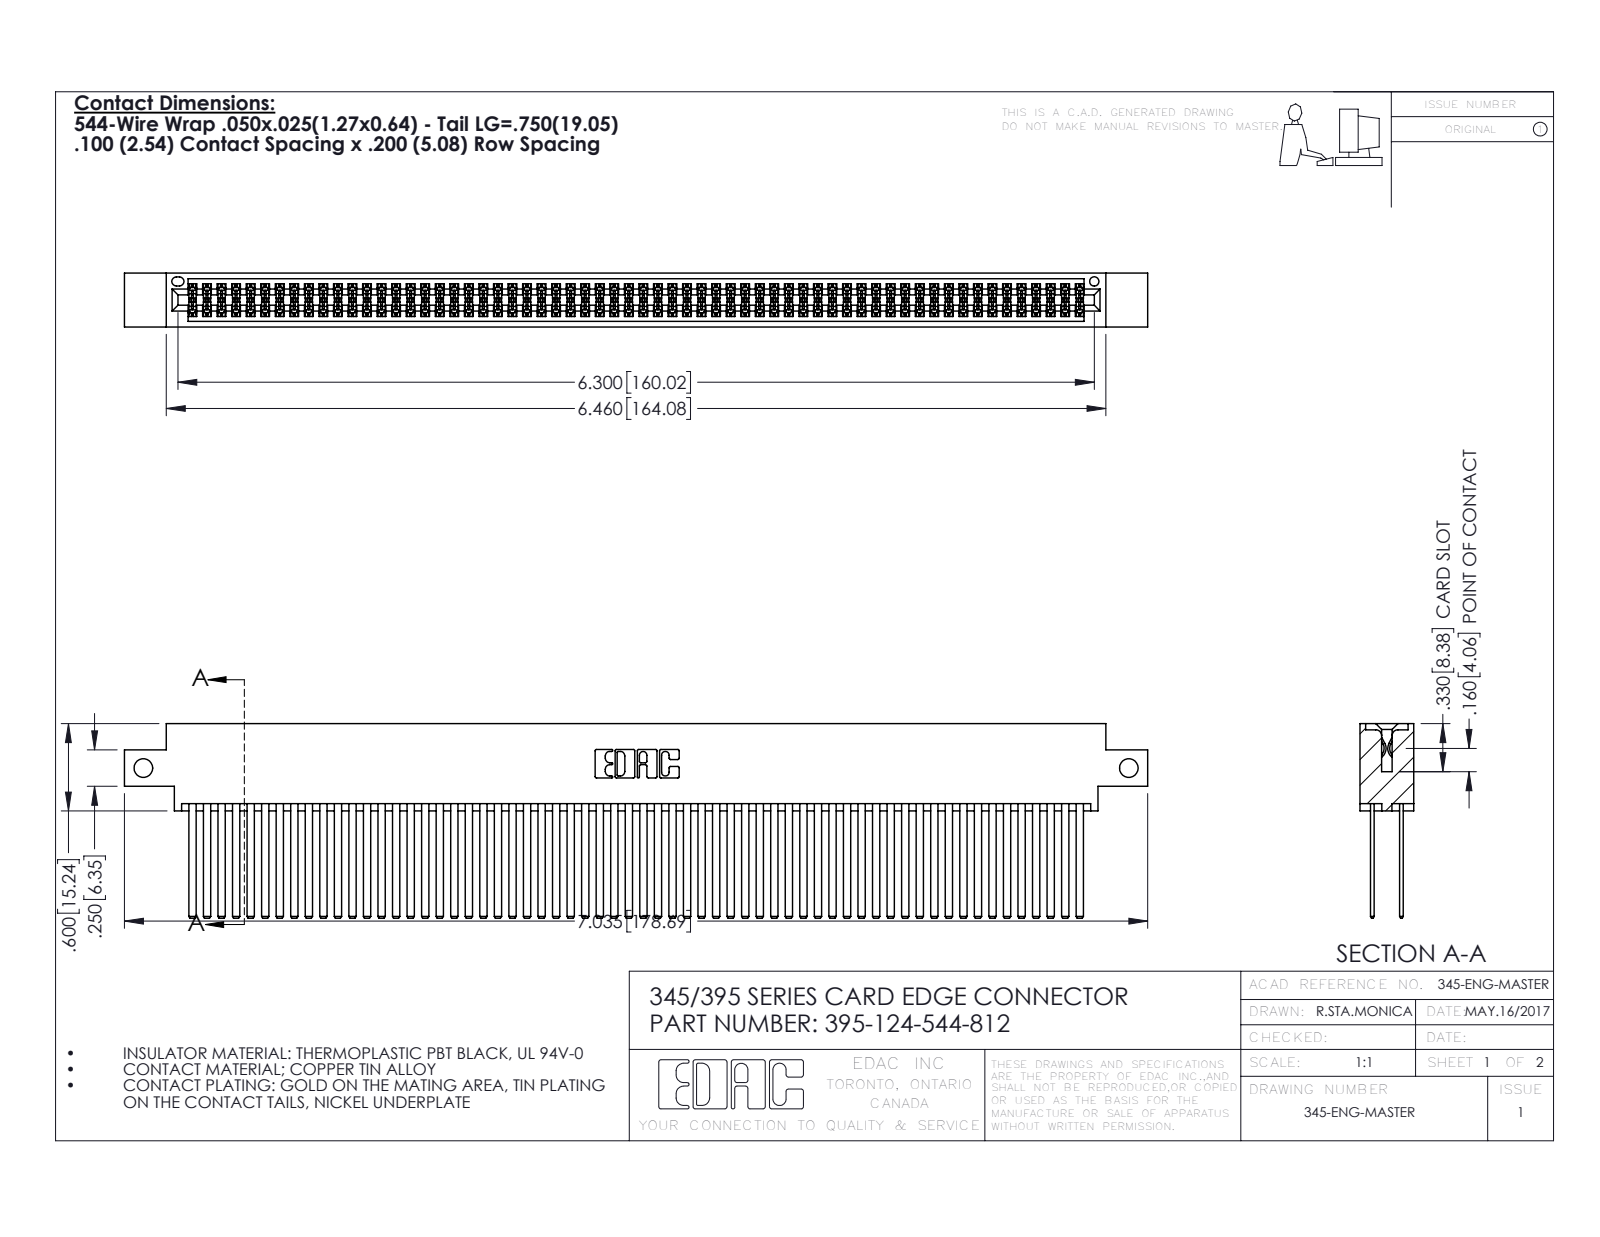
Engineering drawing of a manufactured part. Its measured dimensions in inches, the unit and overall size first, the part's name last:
Units: inches
Overall size (bounding box): 7.035 × 1.337 × 0.37
Round holes (diameter × count): ⌀0.128 ×2, ⌀0.064 ×1
Partial cylindrical surfaces — rounded edges, fillets, slot ends (radius × count): R0.006 ×186, R0.01 ×22, R0.007 ×6, R0.031 ×6, R0.026 ×3, R0.014 ×2, R0.019 ×2, R0.022 ×2
Main face-to-face distances: 0.2, 0.025, 0.298, 0.072, 0.098, 0.272, 0.225, 0.175, 0.37, 0.15
Hole centre spacings: 6.775
Volume: 1.164 in³ · Surface area: 52.23 in²
Bodies: 125 solids, 5586 faces (3680 planar, 1906 cylindrical, 0 other)
Part name (STEP PRODUCT): 395-124-544-812; 345 Part_0.170 Offset - Side Mount; 345-292-001_345-293-144
STEP written by: SolidWorks 2016 (CONFIG_CONTROL_DESIGN)
